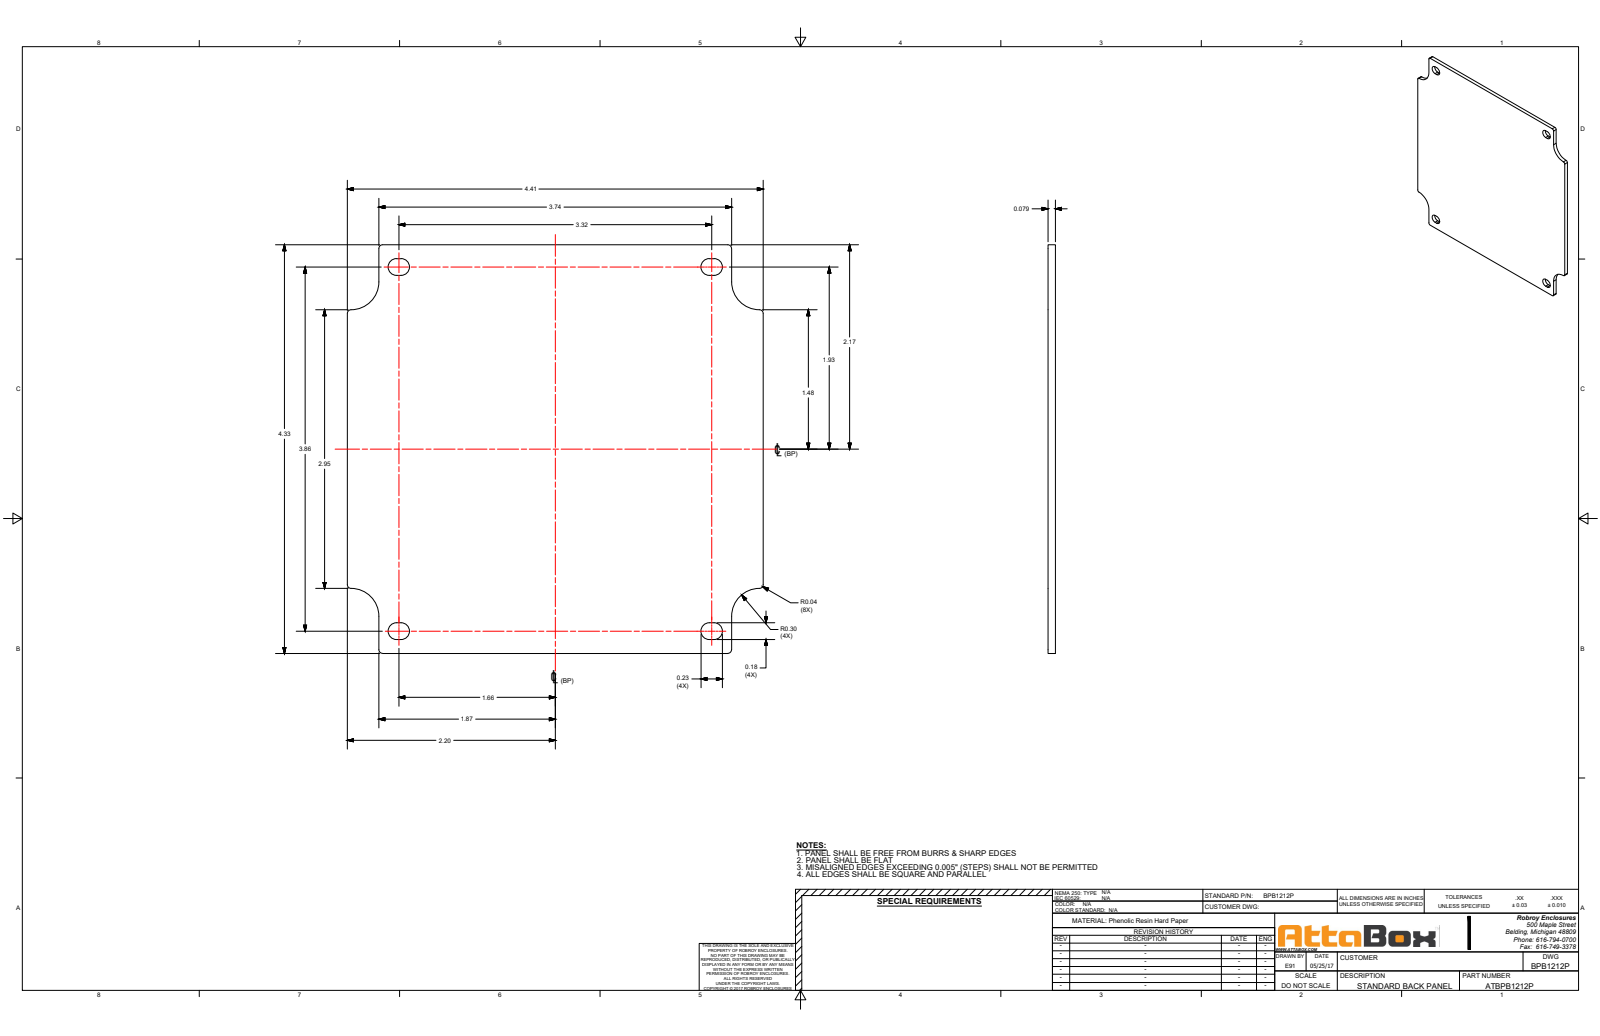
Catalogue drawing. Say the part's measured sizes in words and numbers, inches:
The part is named "BPB1212P". Its 3-D file was written by "SolidWorks 2018 (AUTOMOTIVE_DESIGN)". It is 1 solid with 38 faces: 18 planar, 20 cylindrical and 0 other. Overall it measures 4.409 by 4.331 by 0.079 inches. Its volume is 1.426 cubic inches and its surface area 37.76 square inches. Partial cylindrical surfaces (rounded edges, fillets, slot ends): 8 of radius 0.039, 8 of radius 0.089, 4 of radius 0.295. The main face-to-face distances are 0.079, 4.331, 4.409, 0.335, 4.075, 3.74, 0.148, 0.325, 4.006, 4.183.
